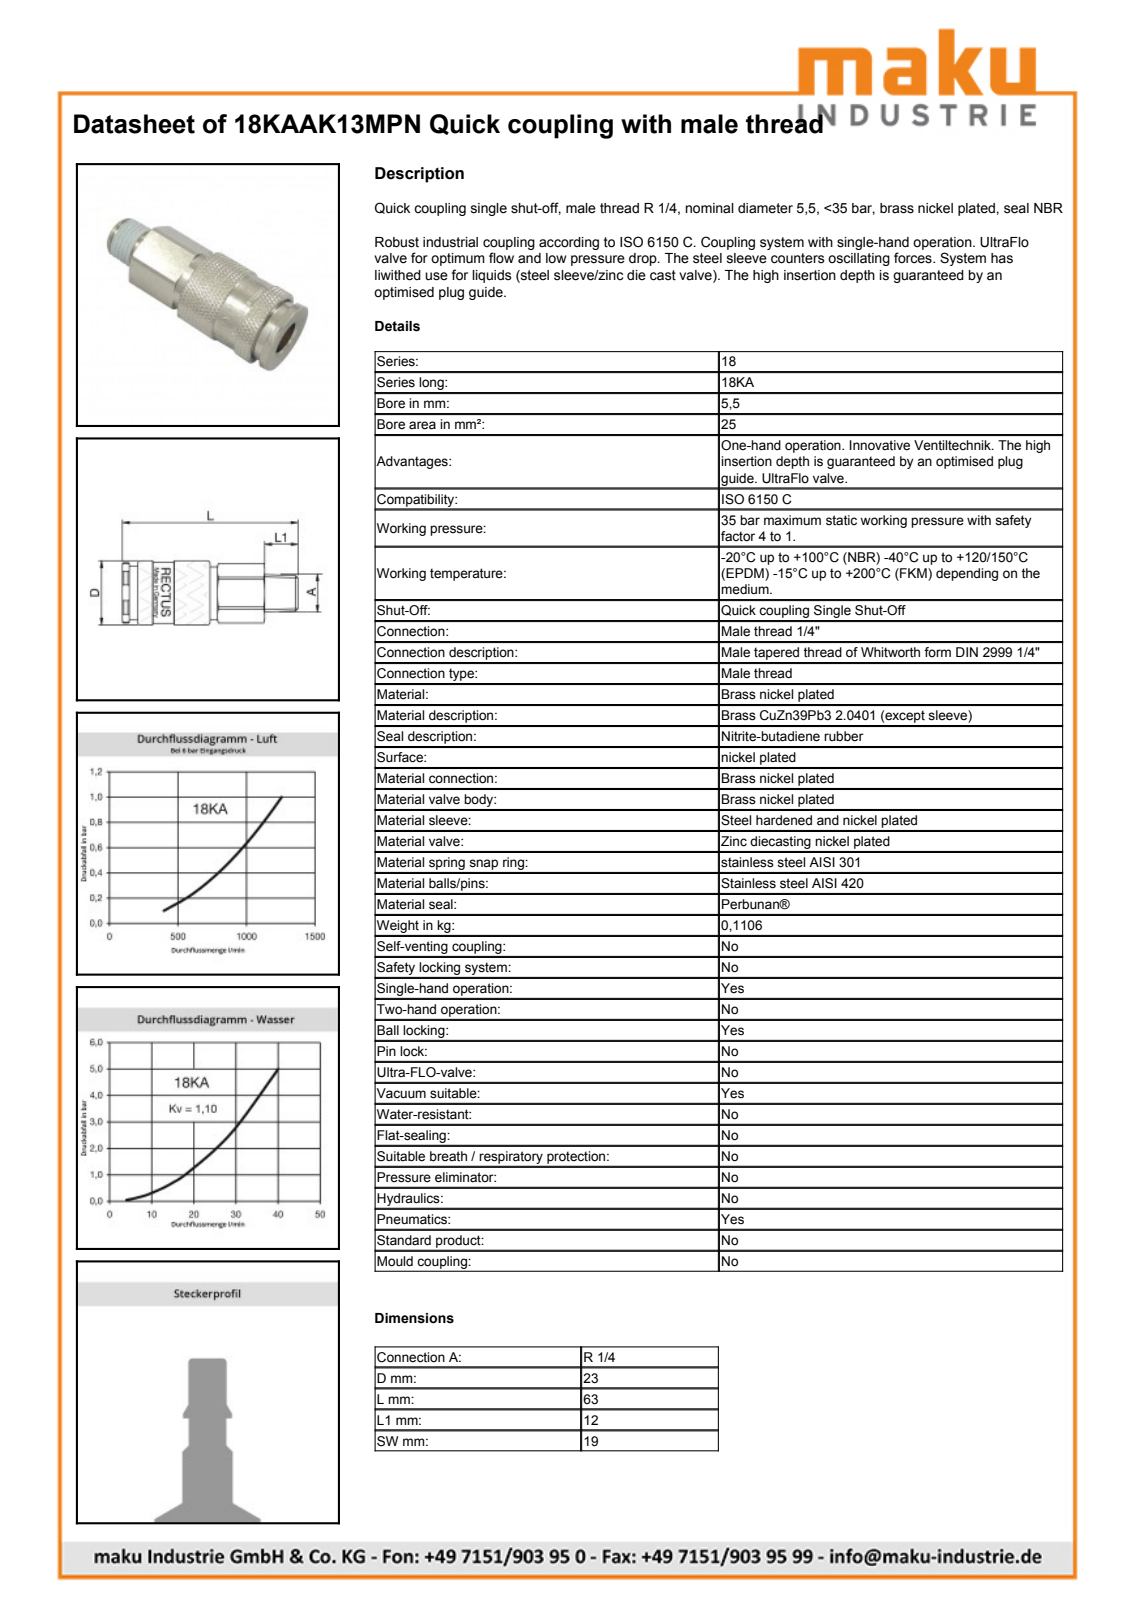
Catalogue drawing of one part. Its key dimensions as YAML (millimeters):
part_name: "D113437; D113439; D113440; D113435 (+7 more)"
step_written_by: "Autodesk Inventor 2013 (AUTOMOTIVE_DESIGN)"
units: millimeters
bodies: {solids: 3, faces: 568, planar: 221, cylindrical: 67, other: 280}
overall_size: [62.9, 23.15, 23.15]
volume: 6267
surface_area: 8541
round_holes:
  - {diameter: 7, count: 1}
  - {diameter: 10, count: 1}
  - {diameter: 14, count: 1}
  - {diameter: 17.63, count: 1}
  - {diameter: 19.35, count: 1}
  - {diameter: 19.5, count: 1}
  - {diameter: 20.47, count: 1}
round_bosses_or_shafts:
  - {diameter: 23.15, count: 1}
  - {diameter: 23.15, count: 1}
  - {diameter: 22, count: 1}
  - {diameter: 19.2, count: 1}
  - {diameter: 18.95, count: 1}
partial_cylinders:
  - {radius: 10.7, count: 1}
  - {radius: 10.99, count: 1}
face_to_face_distances: [19, 4.05, 19.02, 50.9, 46.85, 46.72, 42.67, 4.18, 6.15, 2.1]
